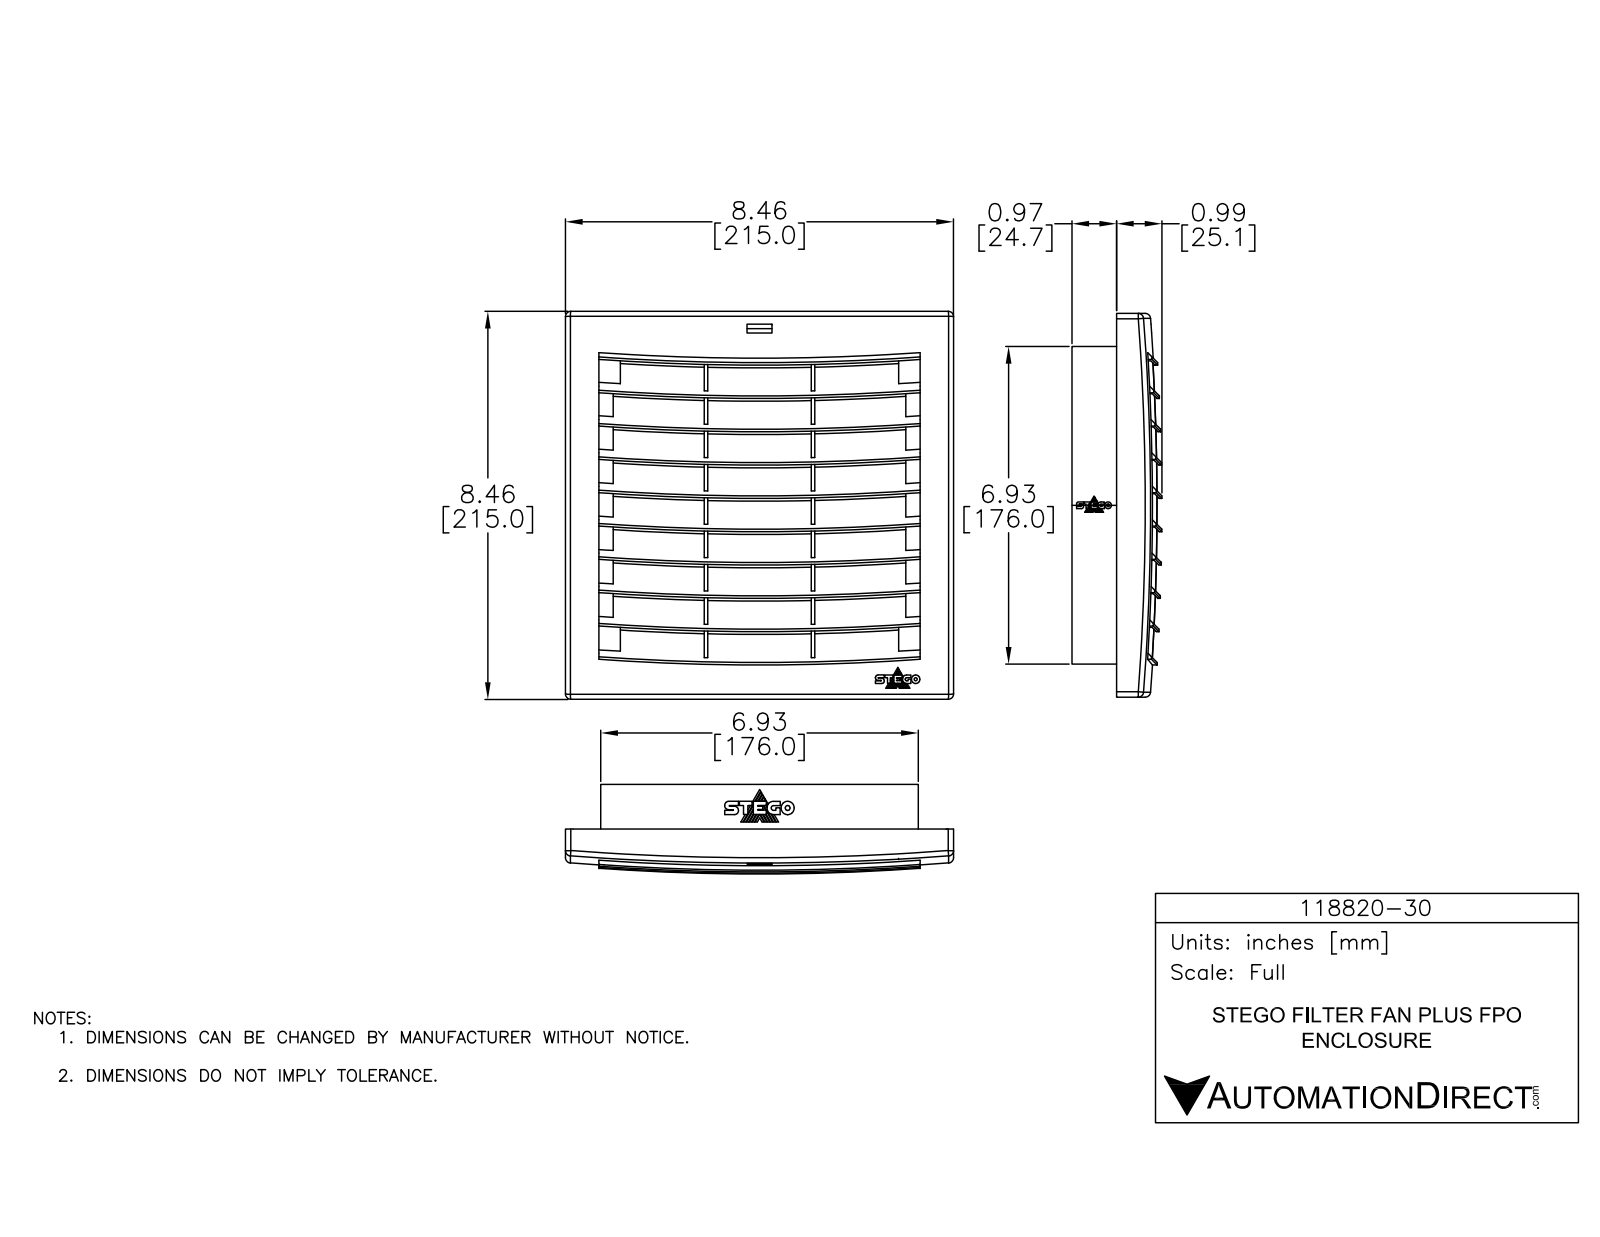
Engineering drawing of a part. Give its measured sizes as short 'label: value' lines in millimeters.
name: 118820-30
written by: SolidWorks 2018 (AUTOMOTIVE_DESIGN)
unit: mm
bodies: 1 solid, 475 faces (255 planar, 220 cylindrical, 0 other)
size: 215 × 215 × 50
volume: 752 000 mm³; area: 272 000 mm²
holes: 1× ⌀79.3, 1× ⌀101.7, 1× ⌀124.2, 1× ⌀149.6
bosses: 1× ⌀130.1, 1× ⌀107.7, 1× ⌀85.3
rounds: 19× R701.4, 4× R5, 1× R18.7, 1× R28.4, 1× R31.4, 1× R582.8
face distances: 23.9, 47.8, 1.5, 11.9, 7.5, 11.9, 25.4, 22.4, 35.8, 71.7
